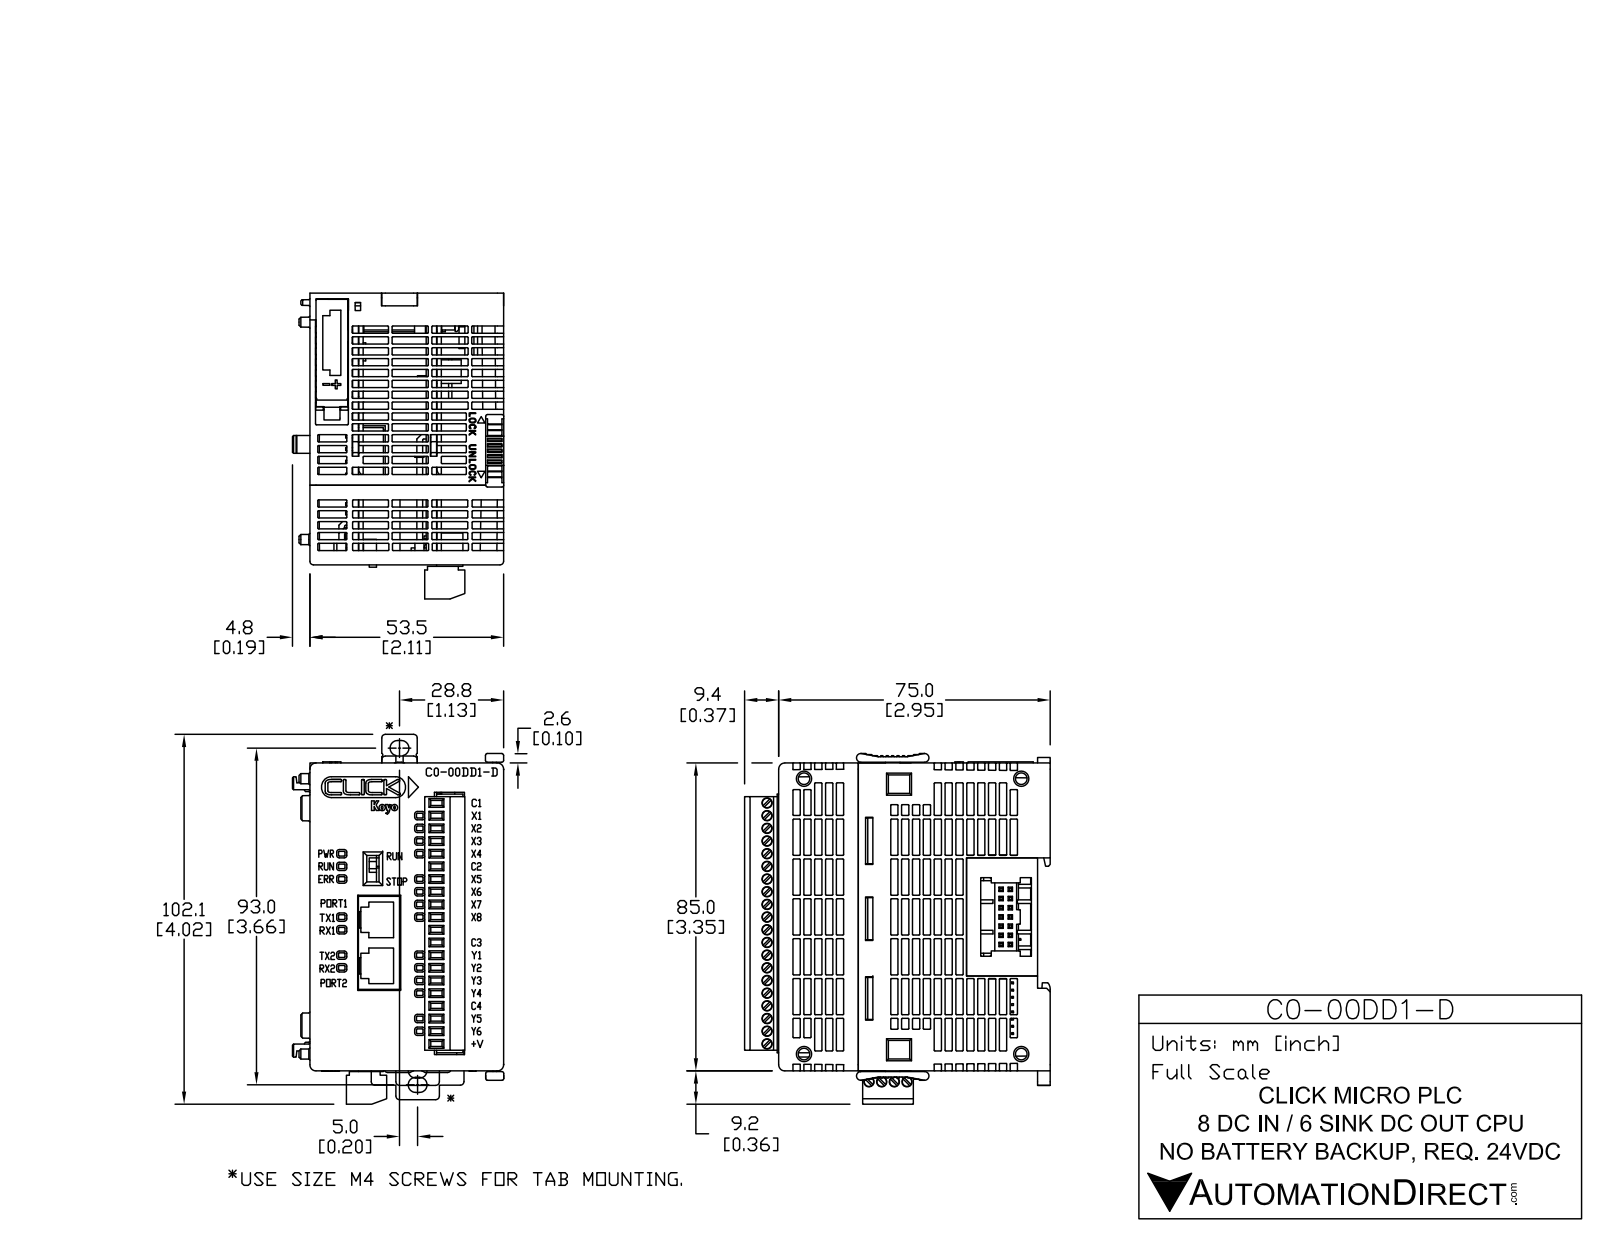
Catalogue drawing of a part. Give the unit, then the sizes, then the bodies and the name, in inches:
Units: inches
Overall size (bounding box): 3.811 × 3.323 × 2.297
Round holes (diameter × count): ⌀0.039 ×24, ⌀0.11 ×24, ⌀0.069 ×1, ⌀0.073 ×1, ⌀0.087 ×1
Round bosses / shafts (diameter × count): ⌀0.102 ×24, ⌀0.11 ×2, ⌀0.085 ×2, ⌀0.075 ×1
Partial cylindrical surfaces — rounded edges, fillets, slot ends (radius × count): R0.008 ×867, R0.012 ×67, R0.02 ×40, R0.11 ×24, R0.039 ×11, R0.047 ×7, R0.067 ×6, R0.004 ×5
Main face-to-face distances: 0.02, 2.087, 2.815, 2.106, 3.327, 3.346, 2.067, 3.307, 0.138, 2.953
Hole centre spacings: 0.138, 0.276, 0.413, 0.551, 0.689, 0.827, 0.965, 1.102
Volume: 20.24 in³ · Surface area: 71.62 in²
Bodies: 1 solid, 5963 faces (4014 planar, 1776 cylindrical, 173 other)
Part name (STEP PRODUCT): C0-00DD1-D
STEP written by: SolidWorks 2009 (AUTOMOTIVE_DESIGN)
